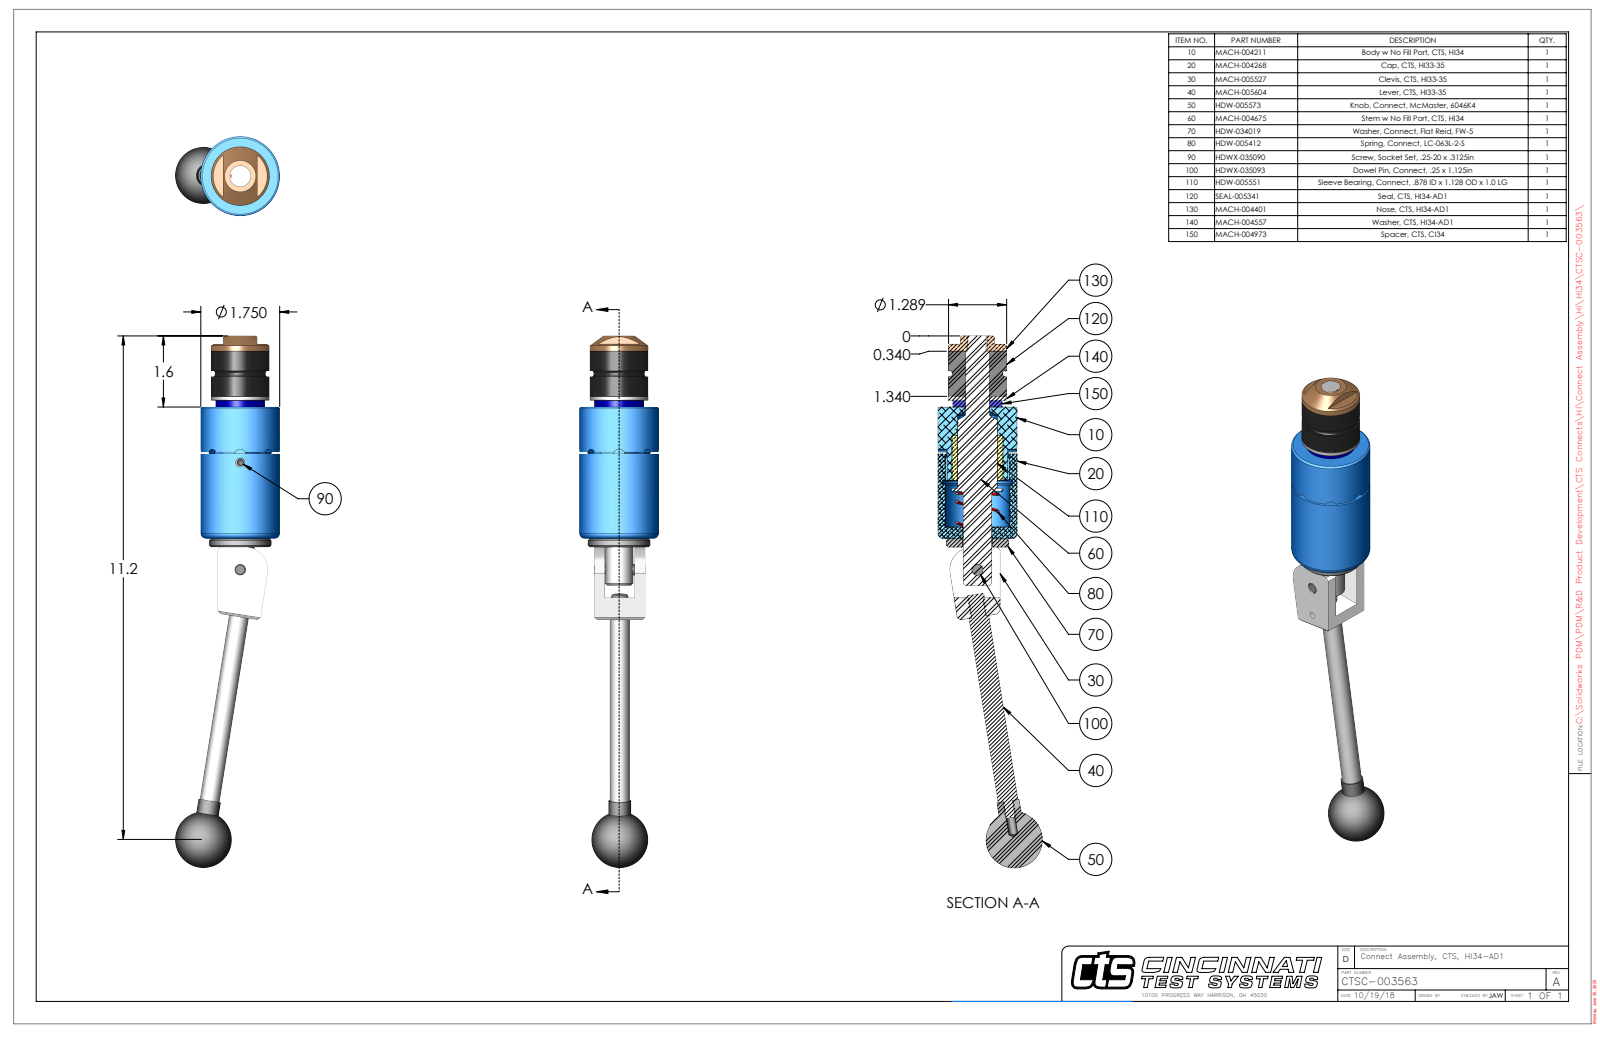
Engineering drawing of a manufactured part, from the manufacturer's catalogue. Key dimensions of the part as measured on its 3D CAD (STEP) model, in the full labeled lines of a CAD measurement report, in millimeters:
Part name (STEP PRODUCT): CTSC-003563
STEP written by: SolidWorks 2023 (AUTOMOTIVE_DESIGN)
Units: millimetres
Bodies: 10 solids, 253 faces (93 planar, 101 cylindrical, 59 other)
Overall size (bounding box): 299.5 × 58.7 × 44.5
Volume: 197 100 mm³ · Surface area: 46 340 mm²
Round holes (diameter × count): ⌀5.1 ×2, ⌀3.8 ×1, ⌀6.3 ×1, ⌀6.4 ×1, ⌀8 ×1, ⌀10.7 ×1, ⌀13.5 ×1, ⌀13.7 ×1, ⌀13.9 ×1, ⌀13.9 ×1, ⌀16.1 ×1, ⌀16.7 ×1
Round bosses / shafts (diameter × count): ⌀12.7 ×2, ⌀11.2 ×2, ⌀6.4 ×2, ⌀44.5 ×1, ⌀35.1 ×1, ⌀32.7 ×1, ⌀27.7 ×1, ⌀15.9 ×1
Partial cylindrical surfaces — rounded edges, fillets, slot ends (radius × count): R3.2 ×4, R0.7 ×2, R12.7 ×1, R17.7 ×1, R21.4 ×1
Main face-to-face distances: 31.4, 25.4, 74.1, 105.5, 6, 80.1, 27.8, 2.4, 3.6, 77.7
Hole centre spacings: 18.8, 60.4, 79.1
